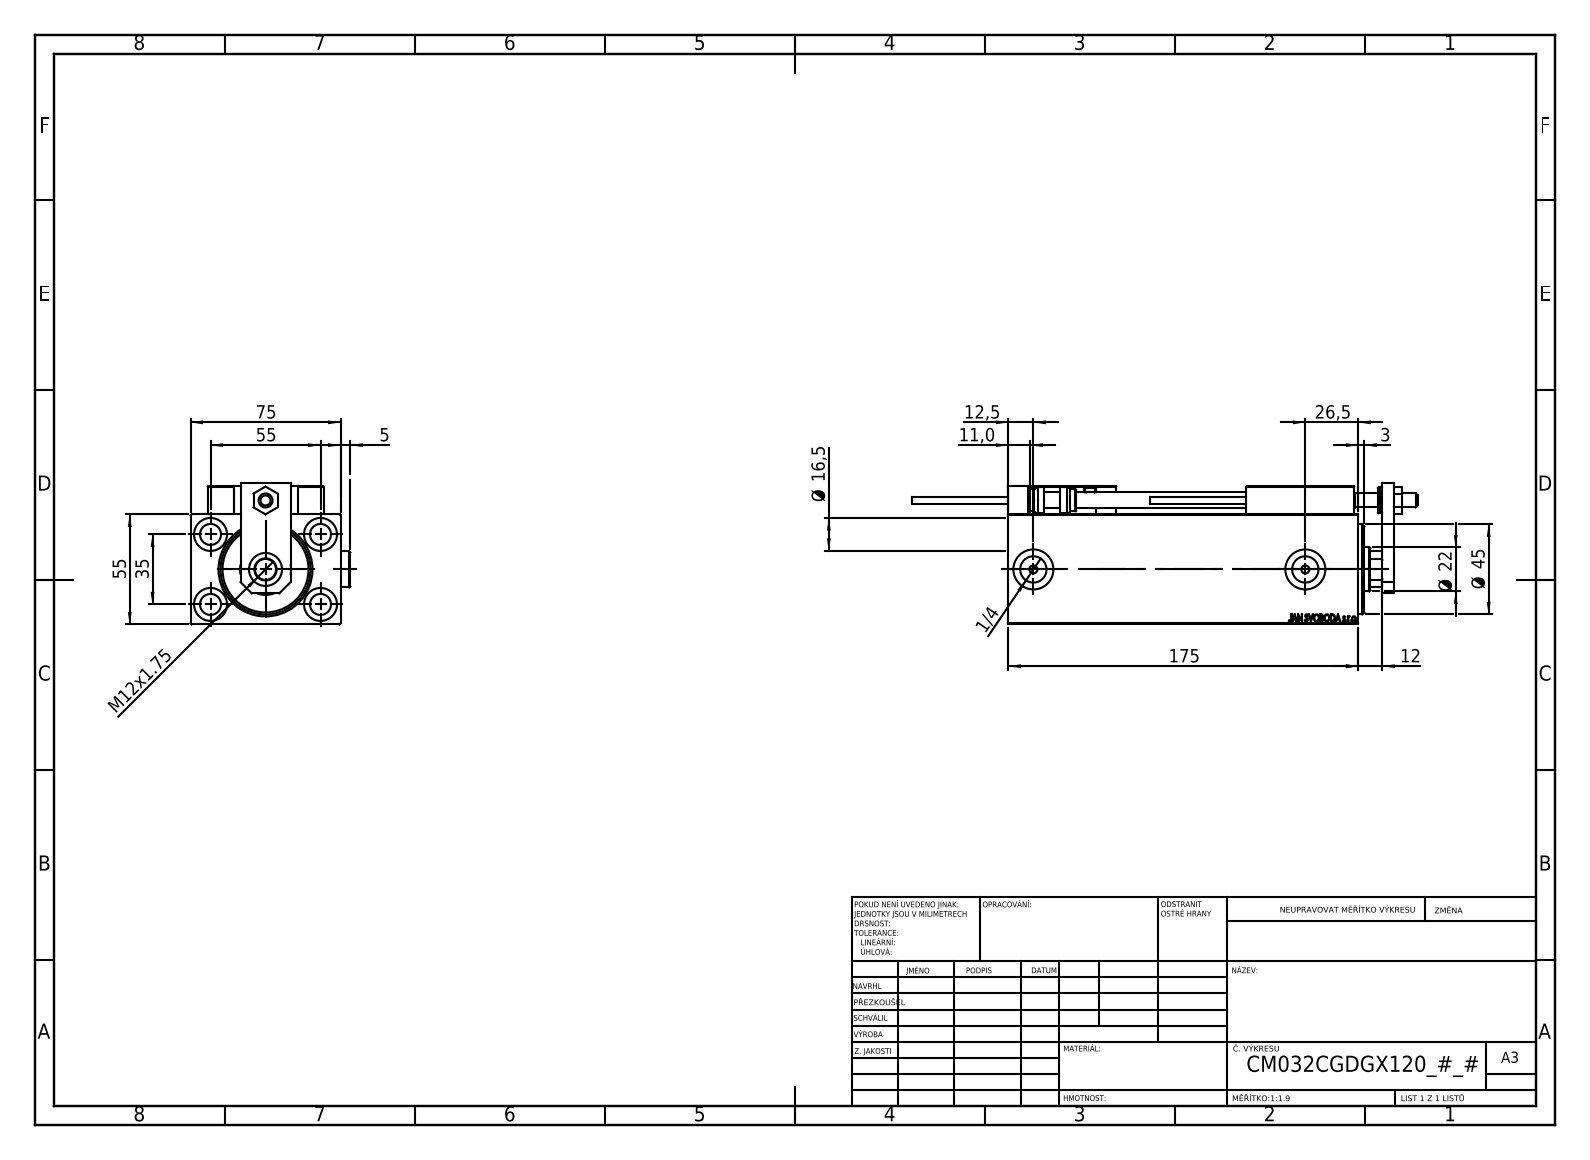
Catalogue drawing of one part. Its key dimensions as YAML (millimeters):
part_name: "ALLEN BOLT D5; ZARAZKA; V450CM_C_Body; TYC_L79 (+7 more)"
step_written_by: "SolidWorks 2019 (CONFIG_CONTROL_DESIGN)"
units: millimeters
bodies: {solids: 25, faces: 1336, planar: 594, cylindrical: 204, other: 538}
overall_size: [252.7, 79.9, 70.5]
volume: 652125
surface_area: 145976
round_holes:
  - {diameter: 4, count: 6}
  - {diameter: 8, count: 5}
  - {diameter: 10.5, count: 5}
  - {diameter: 16.5, count: 5}
  - {diameter: 3.2, count: 4}
  - {diameter: 5, count: 2}
  - {diameter: 13.16, count: 2}
  - {diameter: 20, count: 2}
  - {diameter: 7, count: 1}
  - {diameter: 22, count: 1}
  - {diameter: 25.5, count: 1}
  - {diameter: 32, count: 1}
round_bosses_or_shafts:
  - {diameter: 18, count: 2}
  - {diameter: 5, count: 2}
  - {diameter: 3.8, count: 2}
  - {diameter: 13, count: 1}
  - {diameter: 11, count: 1}
partial_cylinders:
  - {radius: 0.3, count: 30}
  - {radius: 3, count: 2}
  - {radius: 10.5, count: 1}
face_to_face_distances: [55, 75, 14, 10, 12, 5, 7, 69, 15, 25]
hole_center_spacings: [32.6, 11.37, 20, 29.59, 29.69, 32.33, 35, 36.06]
